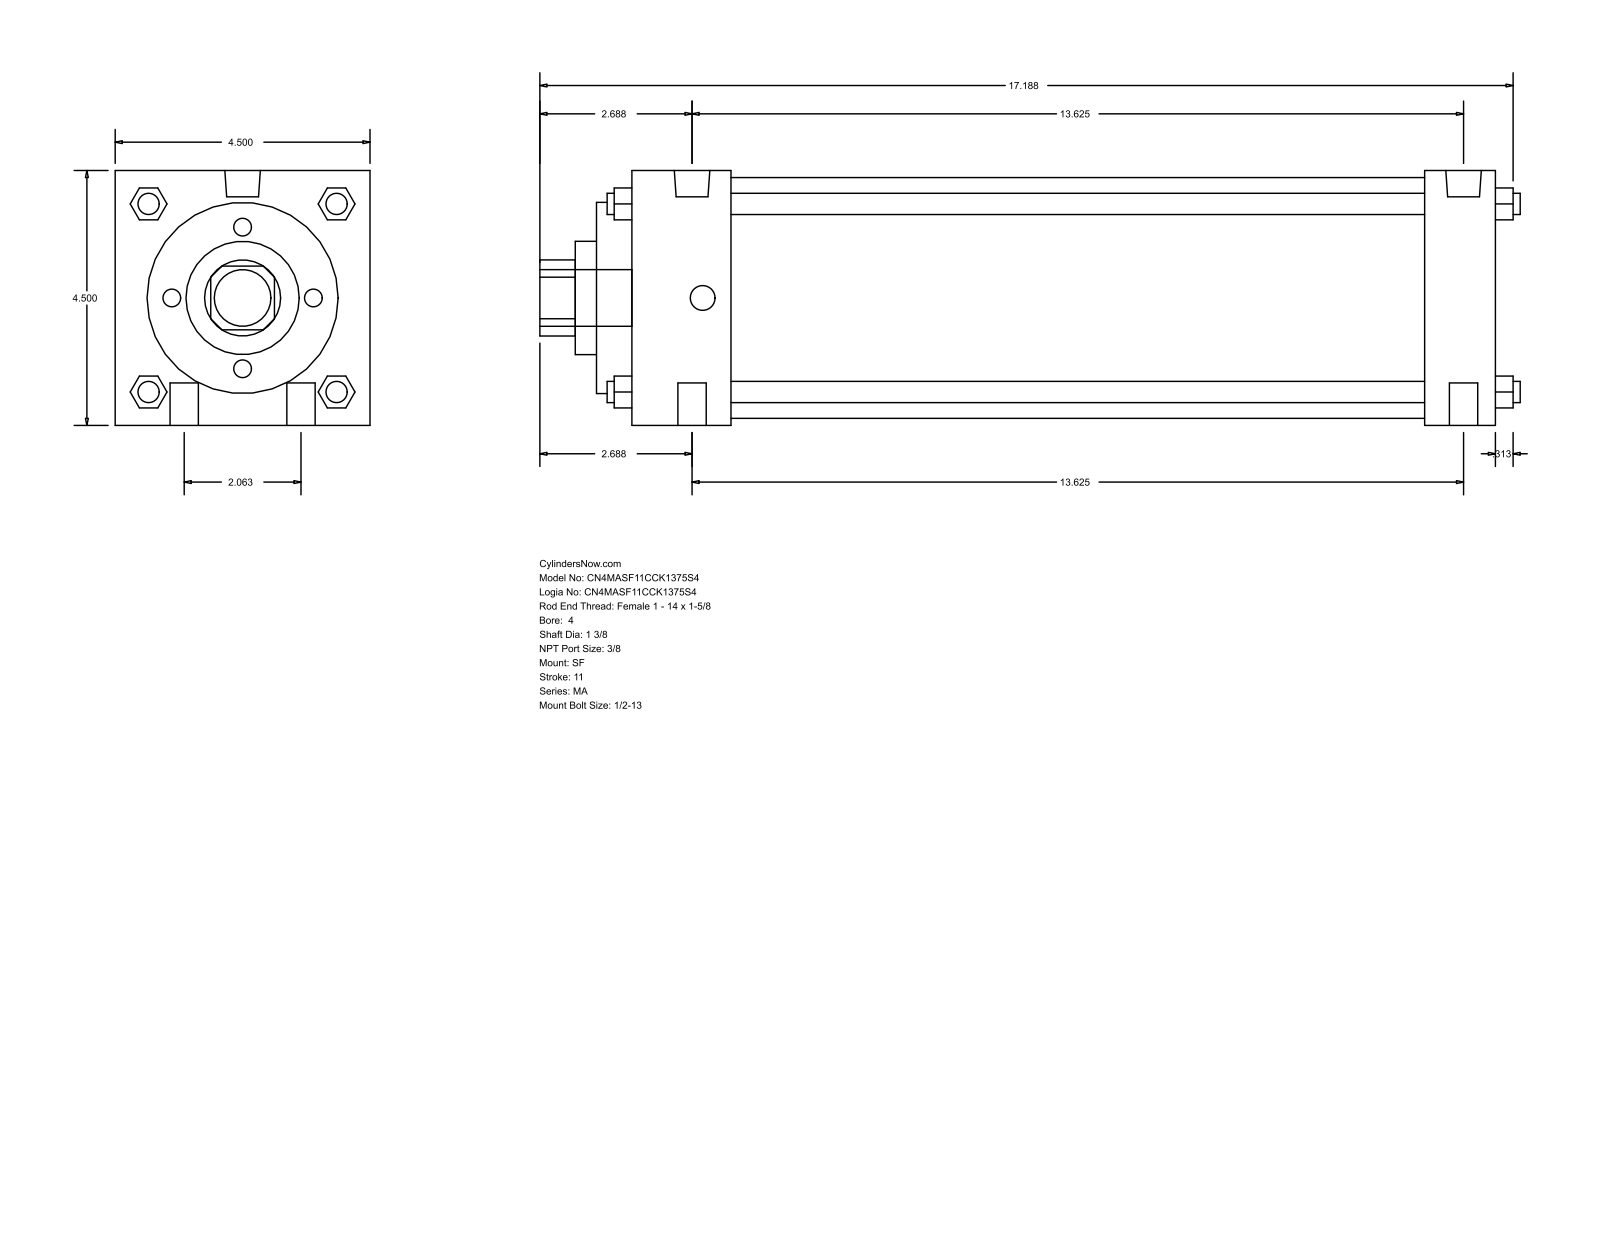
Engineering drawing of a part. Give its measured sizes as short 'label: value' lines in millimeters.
name: MA_SF__0400_1.375
written by: GSSL Pune (CONFIG_CONTROL_DESIGN)
unit: mm
bodies: 0 solids, 126 faces (95 planar, 31 cylindrical, 0 other)
size: 439.74 × 114.3 × 114.3
holes: 1× ⌀34.92, 1× ⌀50.8, 1× ⌀85.72, 1× ⌀107.95
bosses: 4× ⌀12.7, 4× ⌀9.53, 2× ⌀15.93, 2× ⌀11.11, 1× ⌀25.4
rounds: 1× R17.06
face distances: 114.3, 387.35, 403.22, 15.87, 371.48, 355.61, 31.74, 60.32, 44.45, 311.16
